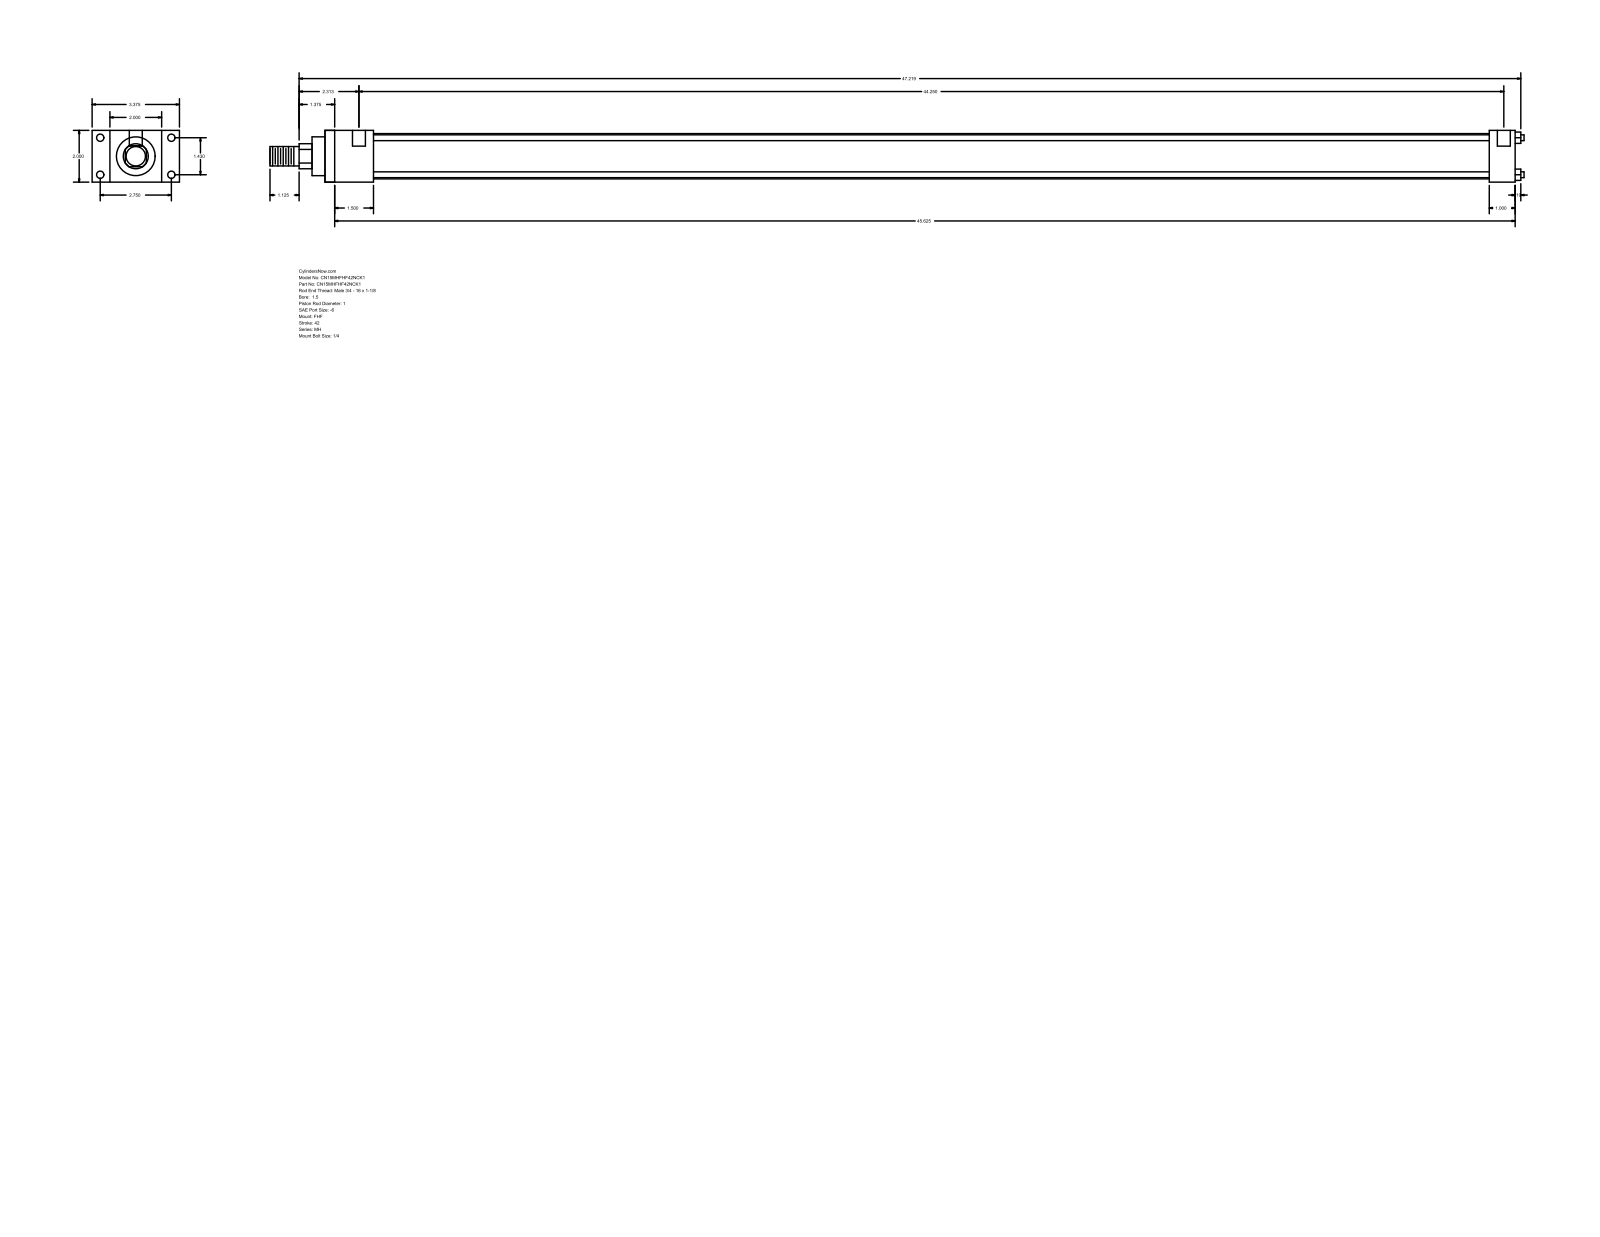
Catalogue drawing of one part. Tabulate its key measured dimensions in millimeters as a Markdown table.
| quantity | value |
| --- | --- |
| part name | MH_FHF__0150_1 |
| STEP written by | GSSL Pune (CONFIG_CONTROL_DESIGN) |
| units | millimeters |
| bodies | 0 solids, 88 faces (60 planar, 28 cylindrical, 0 other) |
| overall size | 1231.11 × 85.72 × 50.8 |
| round holes (diameter × count) | 5.56 × 4, 7.14 × 4, 12.7 × 2 |
| round bosses / shafts (diameter × count) | 5.71 × 4, 44.45 × 1, 38.1 × 1, 25.4 × 1, 19.05 × 1 |
| partial cylindrical surfaces (radius × count) | 12.29 × 1 |
| main face-to-face distances | 50.8, 17.46, 68.26, 47.63, 85.72, 1168.4, 1120.77, 25.4, 1143, 1095.37 |
| hole center spacings | 36.32, 69.84, 78.72, 1127.13, 3.18, 1123.95 |
